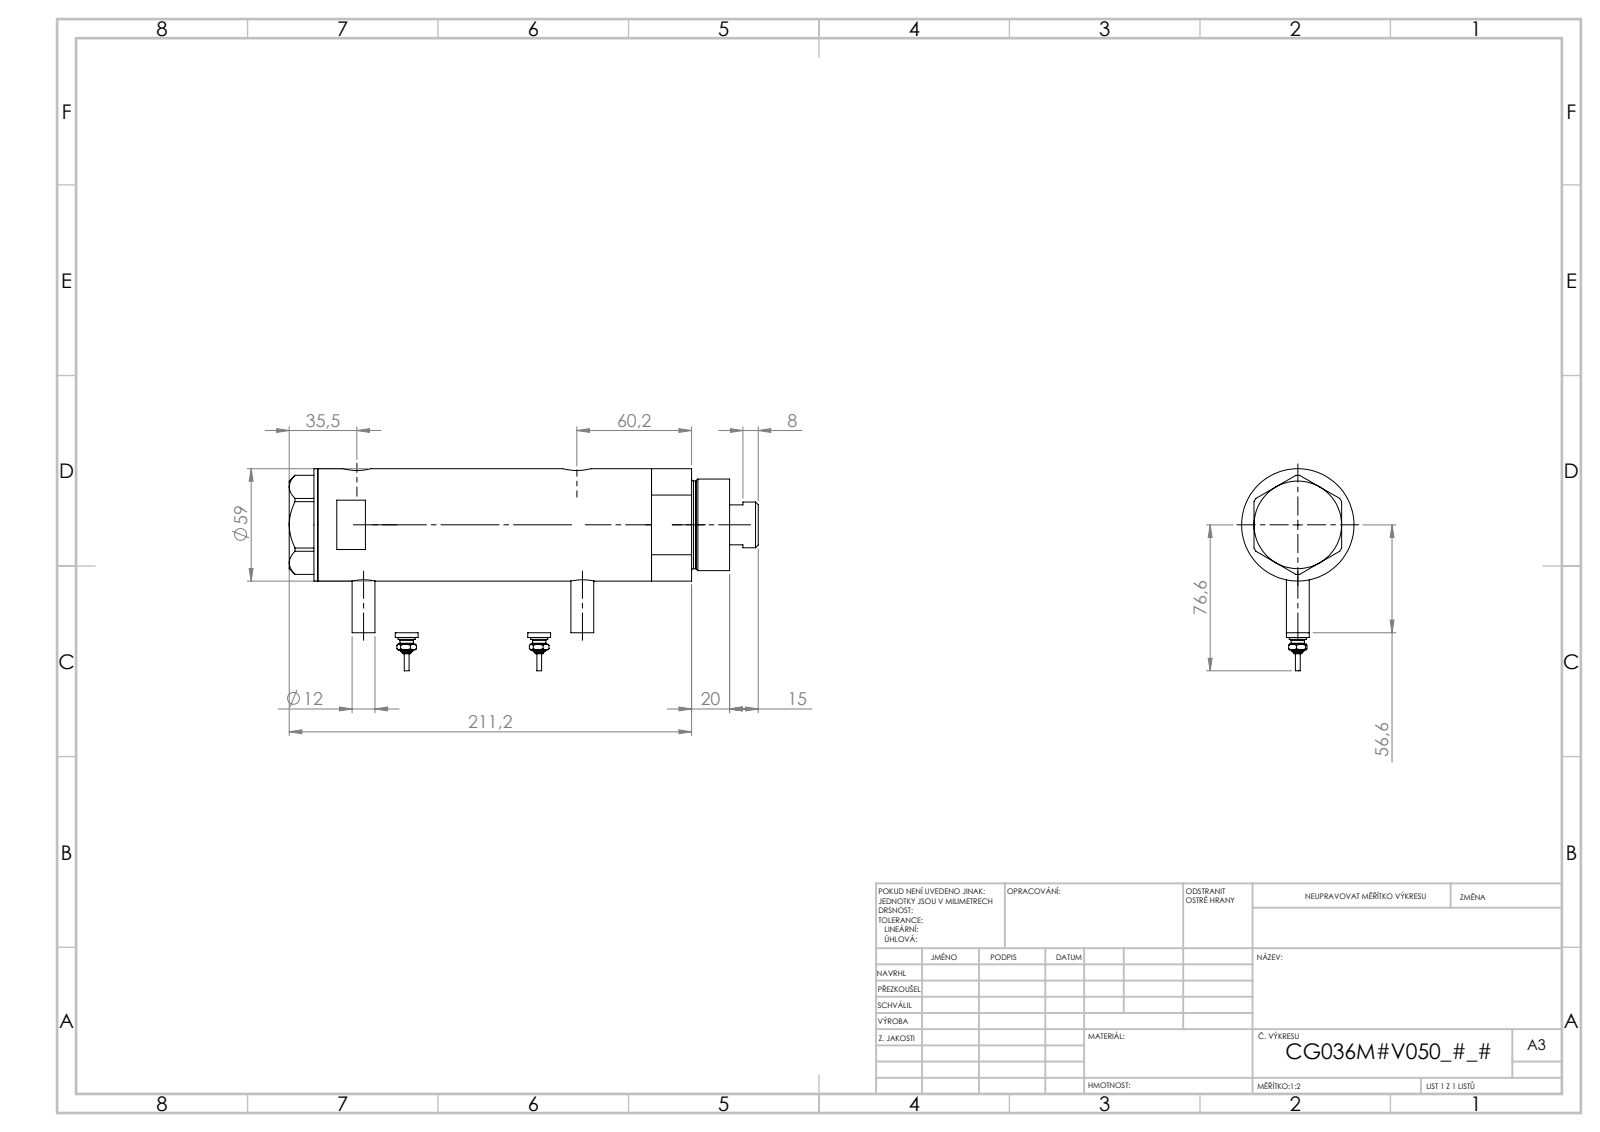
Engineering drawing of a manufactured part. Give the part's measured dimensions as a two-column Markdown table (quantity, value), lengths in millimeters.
| quantity | value |
| --- | --- |
| part name | V270CG_BACK; V270CG_MIDDLE; V270CG_VC; Switch (+1 more) |
| STEP written by | SolidWorks 2019 (CONFIG_CONTROL_DESIGN) |
| units | millimeters |
| bodies | 6 solids, 212 faces (79 planar, 69 cylindrical, 64 other) |
| overall size | 246.2 × 106.1 × 59 |
| volume | 580 147 mm³ |
| surface area | 117 158 mm² |
| round holes (diameter × count) | 9.73 × 2, 12.5 × 2, 15 × 2, 8.5 × 1, 25 × 1, 26.5 × 1, 36 × 1, 40 × 1, 52 × 1 |
| round bosses / shafts (diameter × count) | 12 × 4, 9 × 2, 7 × 2, 4.5 × 2, 2.5 × 2, 59 × 1, 48 × 1, 46 × 1 |
| main face-to-face distances | 137.2, 23.5, 113.7, 15, 38.5, 152.2, 2, 231.2, 216.2, 50 |
| hole center spacings | 2.9, 3.5, 112, 114.9, 115.5, 118.4 |
